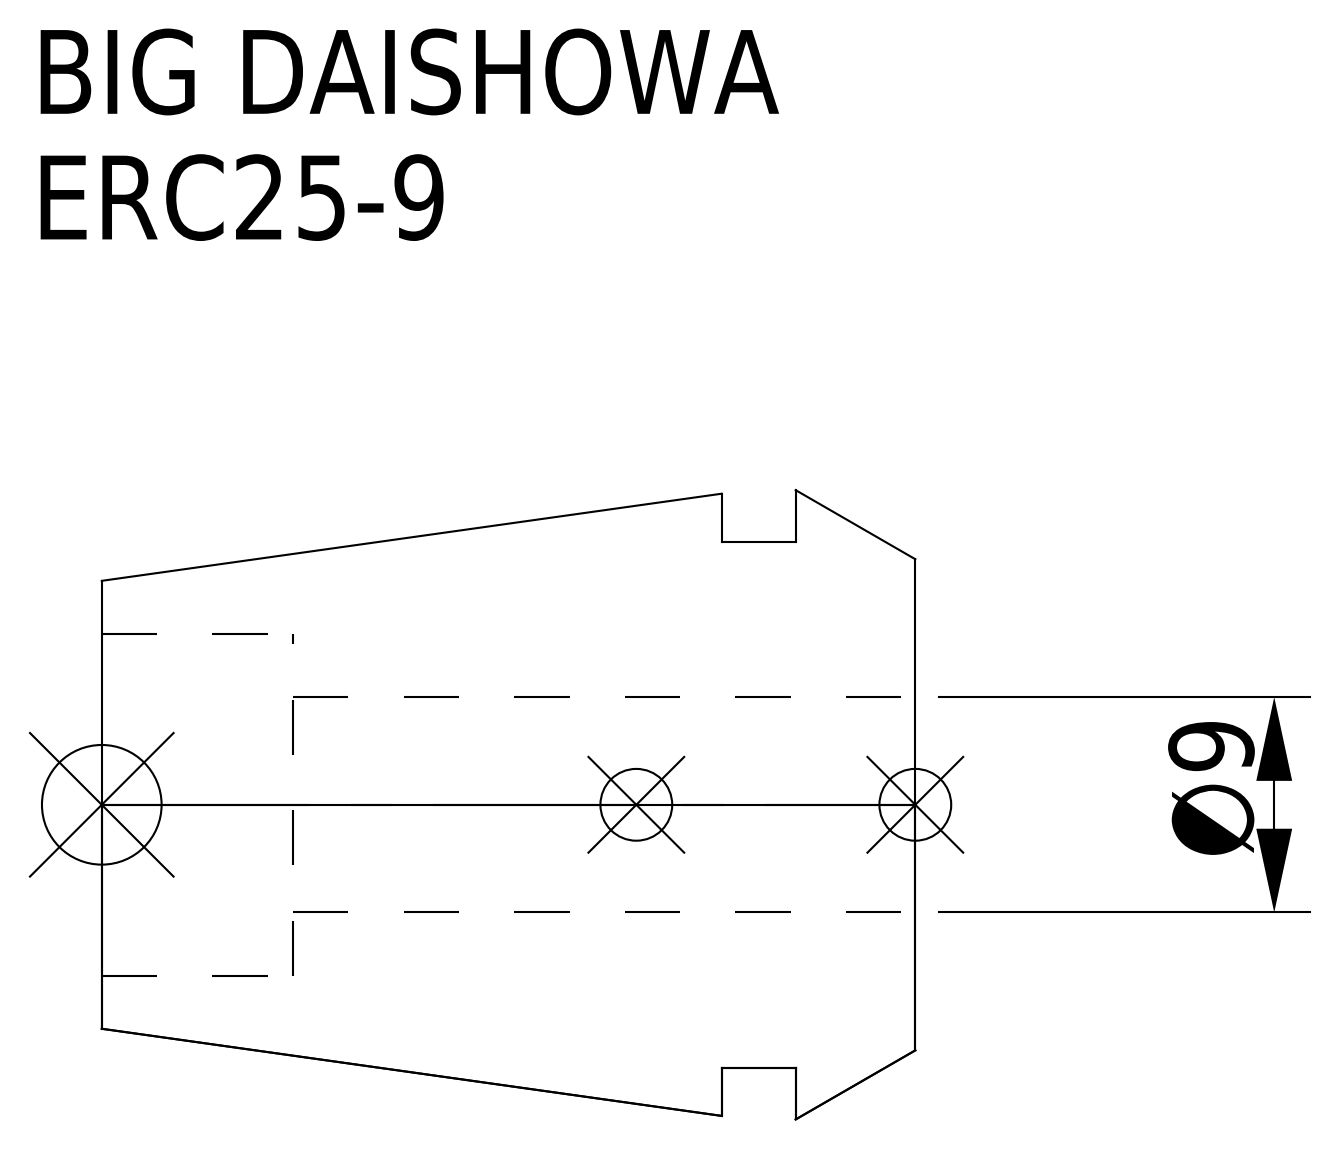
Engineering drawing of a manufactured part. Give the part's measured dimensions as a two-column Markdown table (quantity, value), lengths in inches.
| quantity | value |
| --- | --- |
| part name | ERC25-9 |
| STEP written by | CREO PARAMETRIC BY PTC INC, 2016380 (AUTOMOTIVE_DESIGN) |
| units | inches |
| bodies | 1 solid, 15 faces (5 planar, 6 cylindrical, 4 other) |
| overall size | 1.339 × 1.035 × 1.035 |
| volume | 0.651 in³ |
| surface area | 6.764 in² |
| round holes (diameter × count) | 0.354 × 1, 0.563 × 1 |
| round bosses / shafts (diameter × count) | 0.866 × 1 |
| main face-to-face distances | 0.197, 0.319, 0.122, 1.339, 1.142, 1.02, 1.024, 0.827, 0.705, 0.315 |
